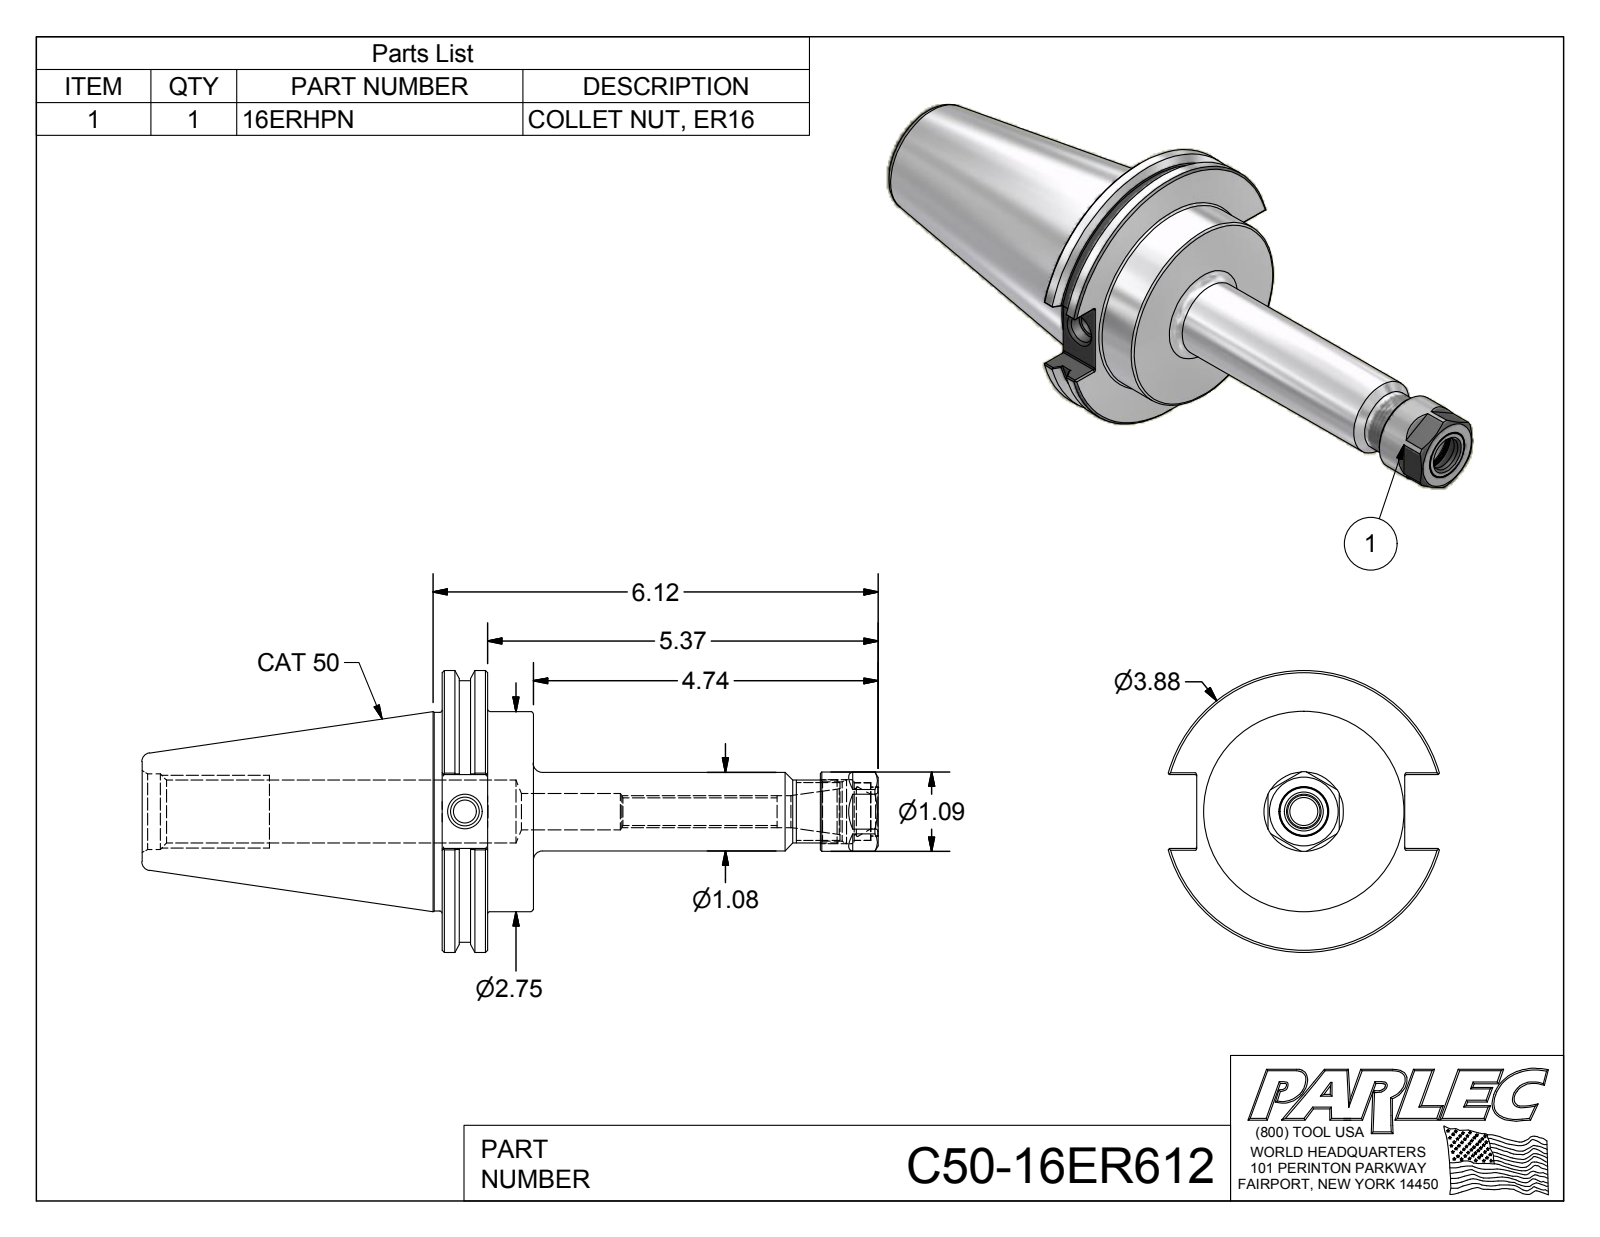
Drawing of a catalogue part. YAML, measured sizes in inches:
part_name: "C50-16ER612; C50-16ER6-1; 16ERHPN"
step_written_by: "Autodesk Inventor 2012 (AUTOMOTIVE_DESIGN)"
units: inches
bodies: {solids: 3, faces: 138, planar: 53, cylindrical: 39, other: 46}
overall_size: [10.12, 3.875, 3.729]
volume: 26.16
surface_area: 102.2
round_holes:
  - {diameter: 0.315, count: 1}
  - {diameter: 0.383, count: 1}
  - {diameter: 0.399, count: 1}
  - {diameter: 0.44, count: 1}
  - {diameter: 0.474, count: 1}
  - {diameter: 0.5, count: 1}
  - {diameter: 0.63, count: 1}
  - {diameter: 0.674, count: 1}
  - {diameter: 0.68, count: 1}
  - {diameter: 0.794, count: 1}
  - {diameter: 0.814, count: 1}
  - {diameter: 0.865, count: 1}
round_bosses_or_shafts:
  - {diameter: 3.875, count: 1}
  - {diameter: 3.594, count: 1}
  - {diameter: 2.75, count: 1}
  - {diameter: 2.73, count: 1}
  - {diameter: 1.092, count: 1}
  - {diameter: 1.08, count: 1}
  - {diameter: 0.866, count: 1}
  - {diameter: 0.79, count: 1}
partial_cylinders:
  - {radius: 0.02, count: 12}
face_to_face_distances: [1.255, 0.625, 0.63, 4.125, 4.75, 5.38, 0.98, 10.12, 5.995, 5.37]
